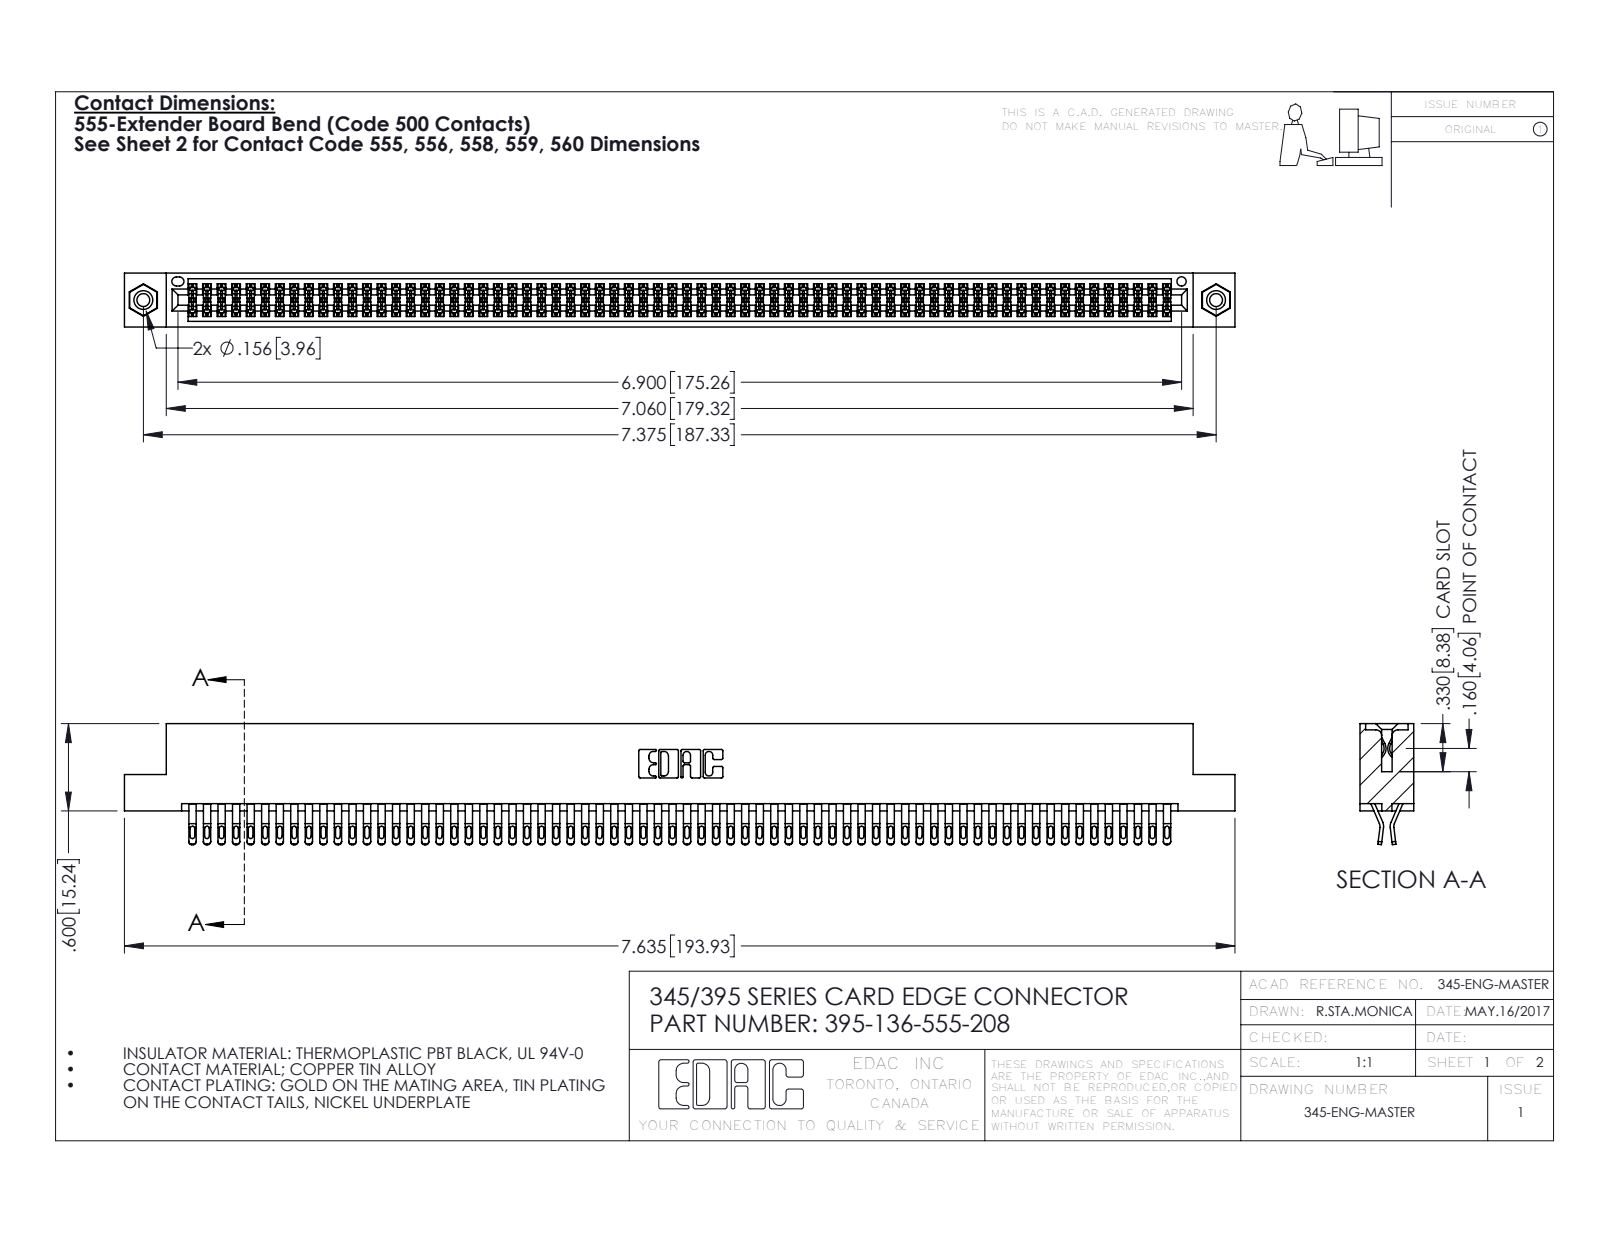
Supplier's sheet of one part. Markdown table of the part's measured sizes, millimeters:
| quantity | value |
| --- | --- |
| part name | 395-136-555-208; 345 Part_Flush Mounting Lugs - 0.156 Dia-TI; 345-250-001_345-250-003-102; 345-292-001_555 Tail |
| STEP written by | SolidWorks 2016 (CONFIG_CONTROL_DESIGN) |
| units | millimeters |
| bodies | 139 solids, 7802 faces (4328 planar, 3458 cylindrical, 16 other) |
| overall size | 193.9 × 21.1 × 9.4 |
| volume | 19 470 mm³ |
| surface area | 30 660 mm² |
| round holes (diameter × count) | 2.3 × 2, 3.2 × 2, 4 × 2, 1.6 × 1 |
| round bosses / shafts (diameter × count) | 3.9 × 2 |
| partial cylindrical surfaces (radius × count) | 0.4 × 340, 0.5 × 272, 0.2 × 204, 0.3 × 22, 0.2 × 6, 0.8 × 6, 0.7 × 3, 0.3 × 2 |
| main face-to-face distances | 1.8, 7.6, 0.6, 9.4, 5.1, 2.5, 6.9, 5.7, 4.4, 3.8 |
| hole center spacings | 6.9, 181.3, 187.3 |
